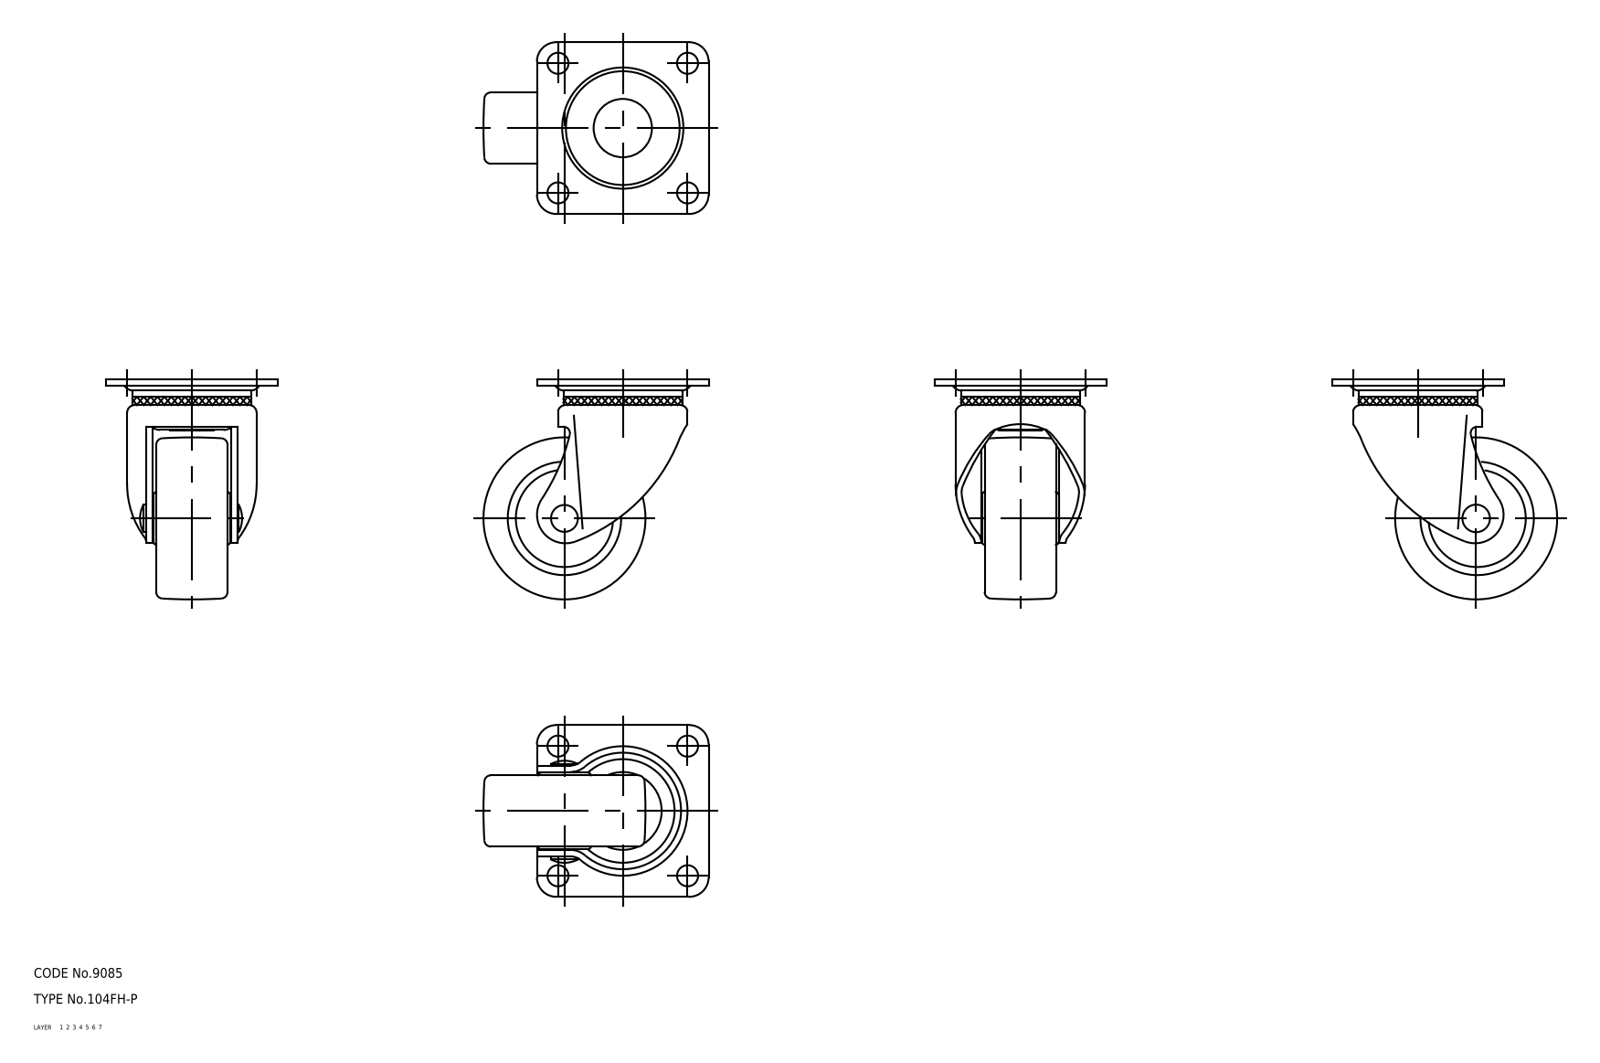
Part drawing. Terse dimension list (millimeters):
name: wheel; mounting plate; main shaft; axle (+1 more)
written by: CADfix (AUTOMOTIVE_DESIGN)
unit: mm
bodies: 5 solids, 213 faces (0 planar, 0 cylindrical, 213 other)
size: 69.5 × 68 × 53
volume: 59 171 mm³; area: 26 060 mm²
